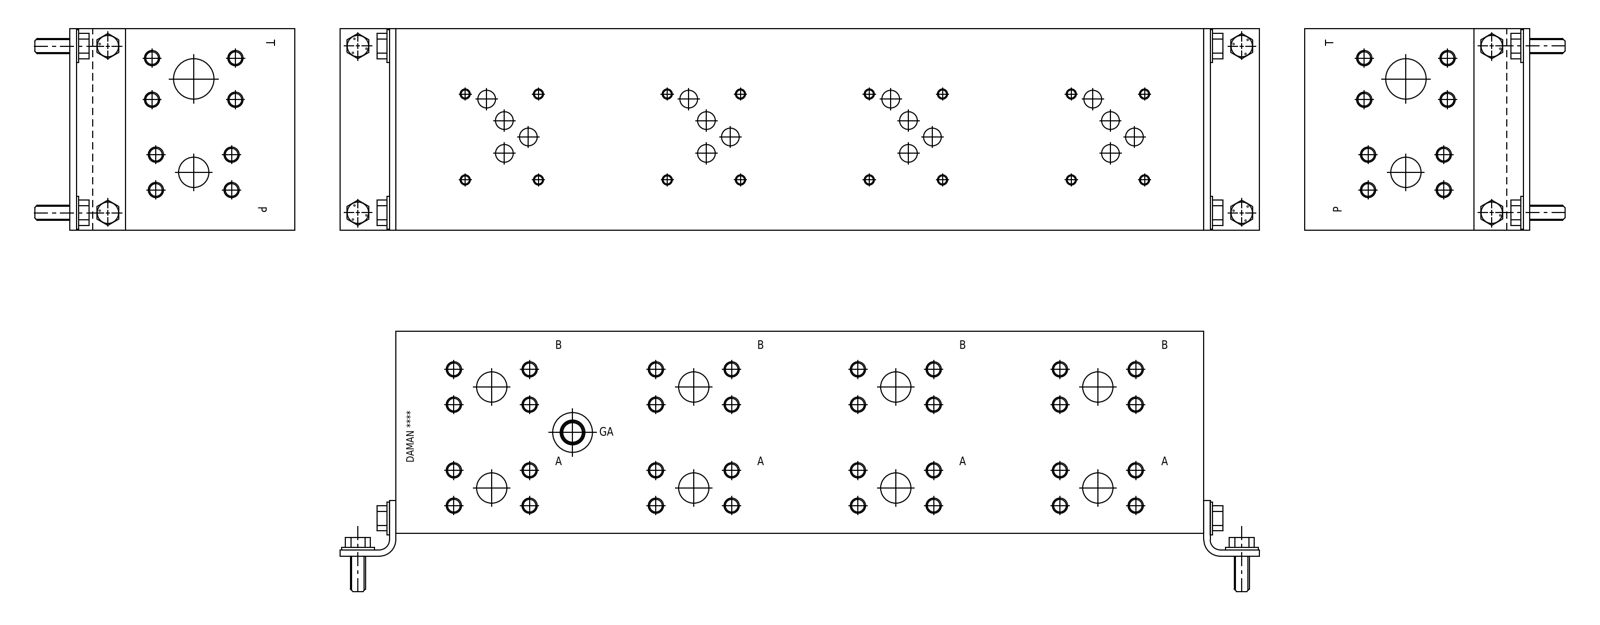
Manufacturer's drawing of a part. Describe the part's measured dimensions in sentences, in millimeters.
The part is named "D05HP045F". Its 3-D file was written by "Autodesk Inventor 2019 (AUTOMOTIVE_DESIGN)". It is 1 solid with 885 faces: 458 planar, 169 cylindrical and 258 other. Overall it measures 508 by 127 by 127 millimeters. Its volume is 7 926 000 cubic millimeters and its surface area 378 397 square millimeters. Round holes: 42 of diameter 7.92, 42 of diameter 9.53, 16 of diameter 5.11, 16 of diameter 6.35, 16 of diameter 11.13, 9 of diameter 19.05, 1 of diameter 12.29, 1 of diameter 12.9, 1 of diameter 14.27, 1 of diameter 15.6, 1 of diameter 25.02, 1 of diameter 25.4. The main face-to-face distances are 127, 508, 25.4, 101.6, 482.6, 24.61, 0.79, 126.21, 1, 24.4. The hole center spacings are 127, 254, 141.99, 26.26, 261.82, 52.51, 63.5, 78.3.
